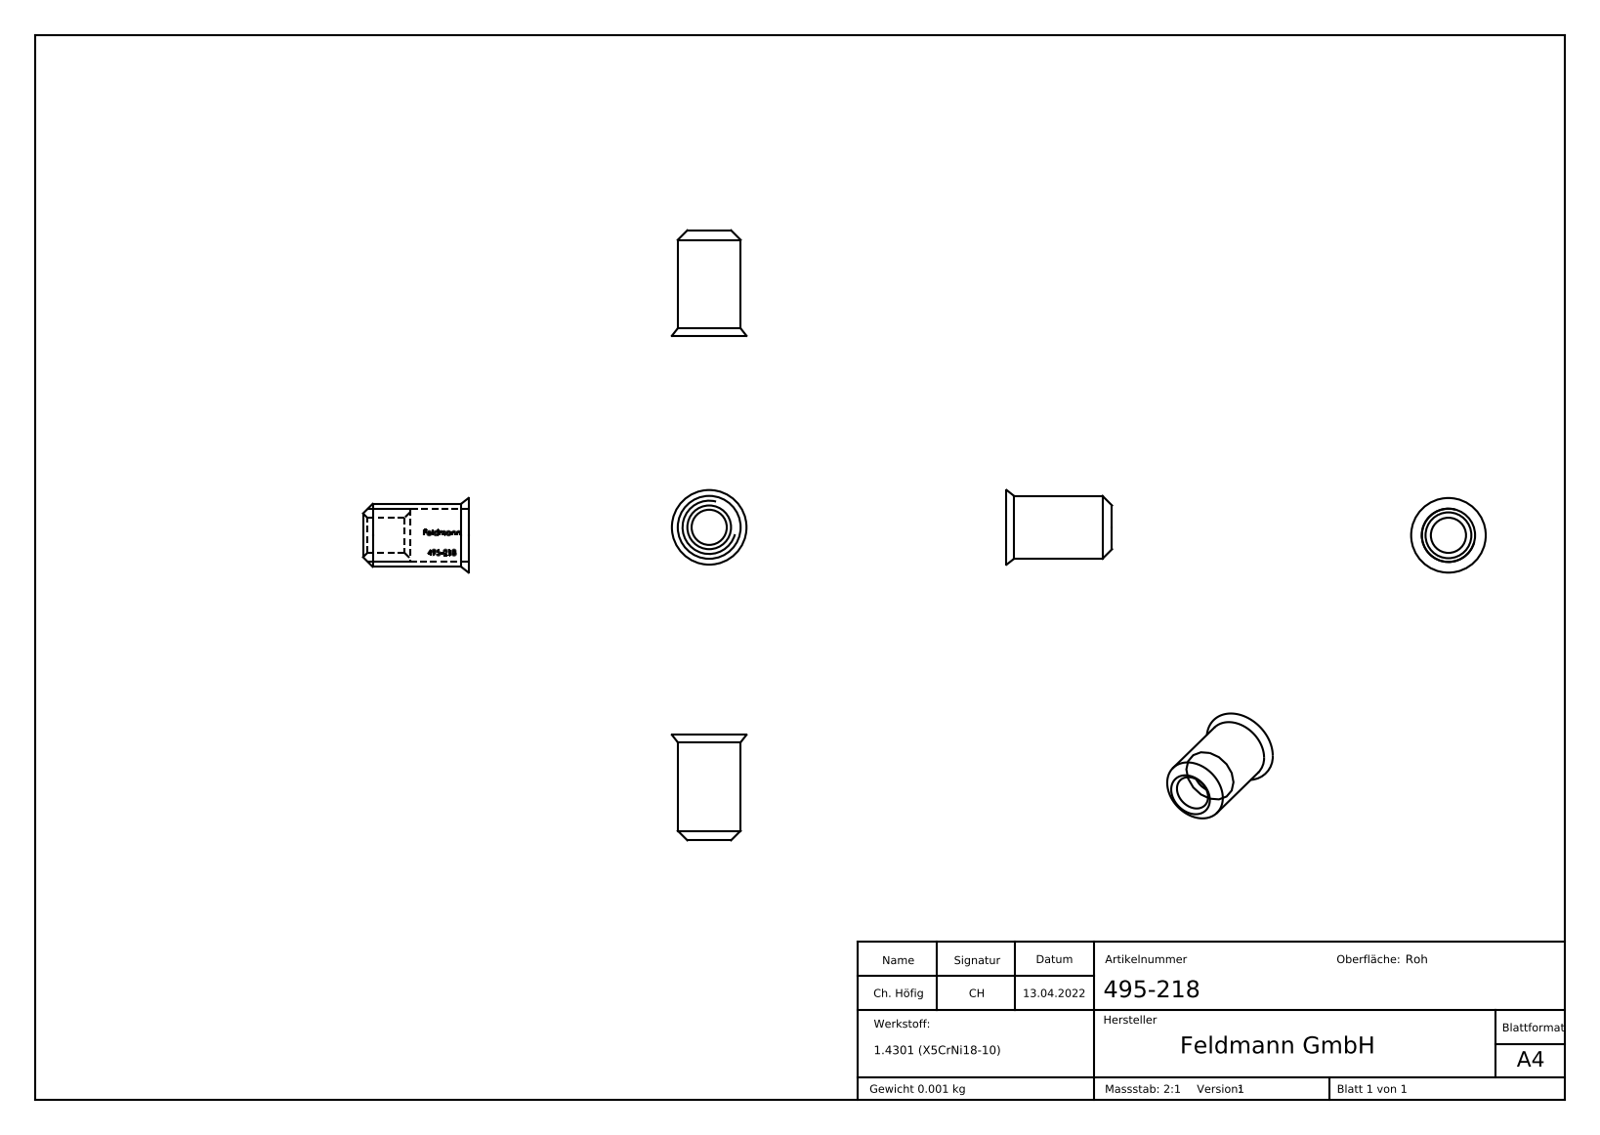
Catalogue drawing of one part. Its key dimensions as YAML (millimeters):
part_name: "495-218"
step_written_by: "SolidWorks 2018 (CONFIG_CONTROL_DESIGN)"
units: millimeters
bodies: {solids: 1, faces: 217, planar: 94, cylindrical: 31, other: 92}
overall_size: [9.9, 7, 7]
volume: 120
surface_area: 357
round_holes:
  - {diameter: 3.3, count: 1}
  - {diameter: 5, count: 1}
round_bosses_or_shafts:
  - {diameter: 5.9, count: 1}
partial_cylinders:
  - {radius: 2.6, count: 1}
face_to_face_distances: [5.5, 0.66, 1.83, 1.35, 1.88, 1.74, 1.19, 1.78, 1.67, 1.79]
